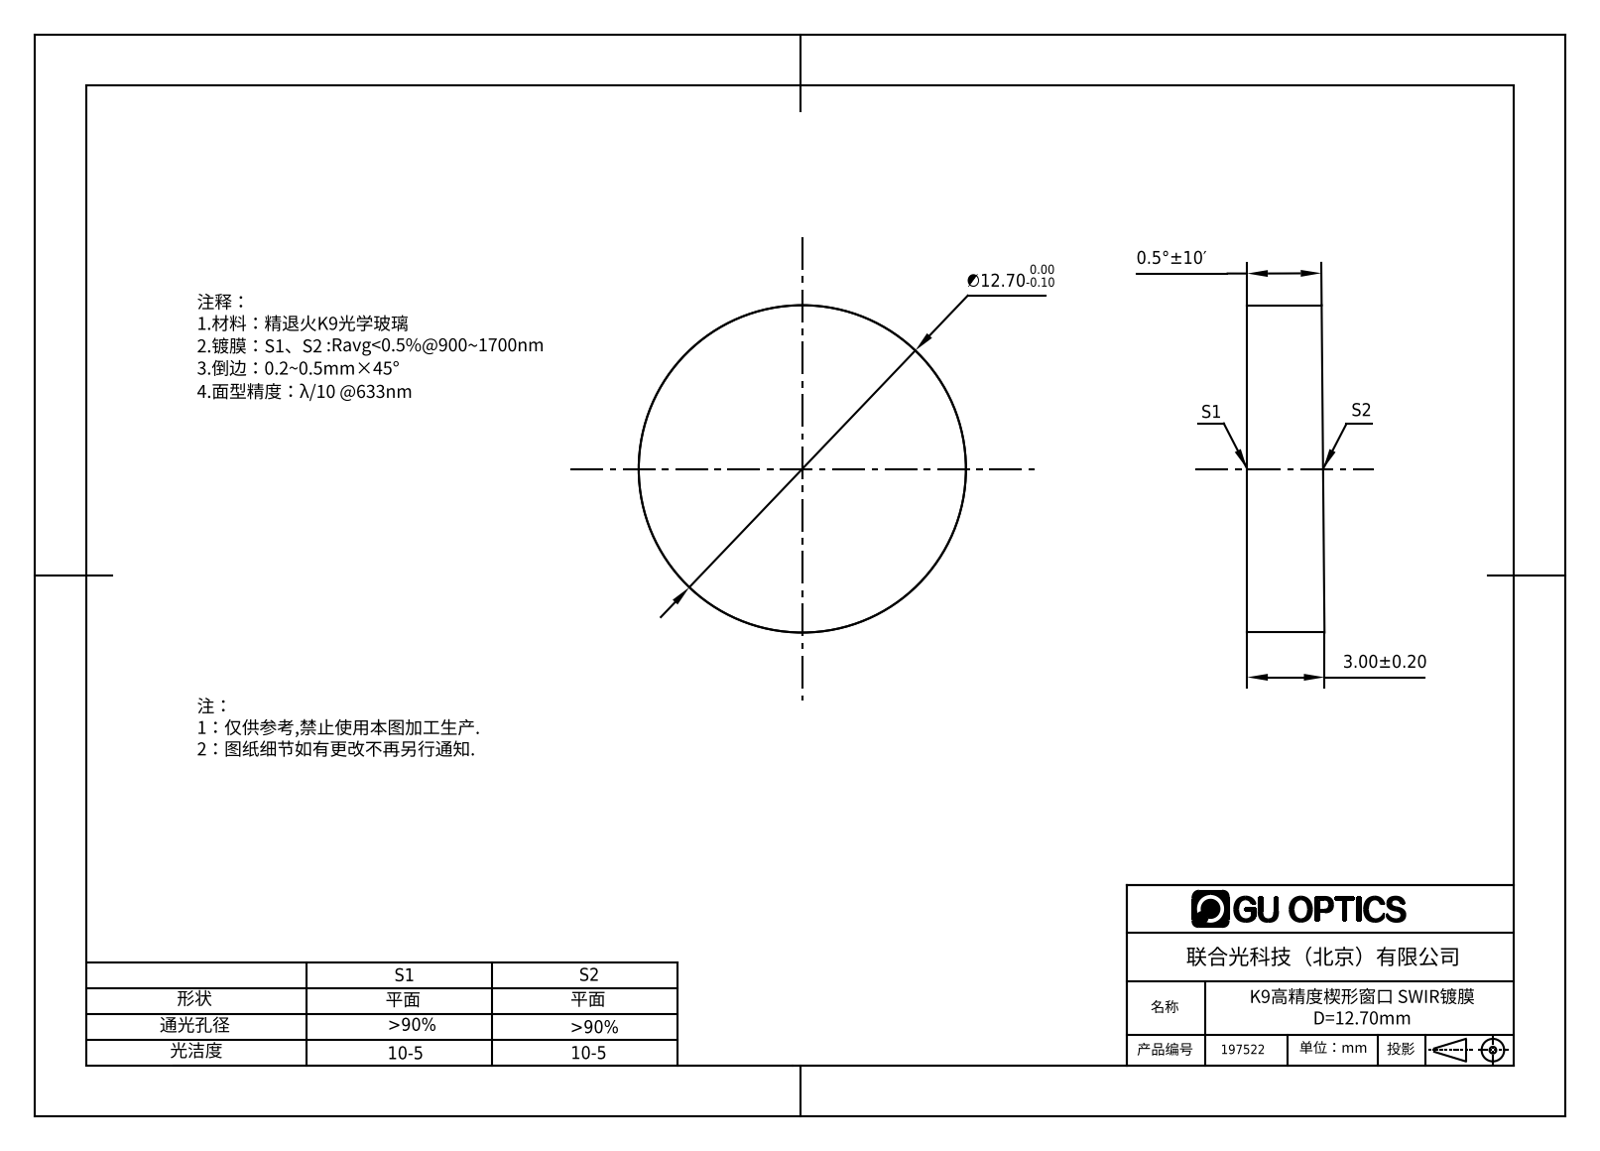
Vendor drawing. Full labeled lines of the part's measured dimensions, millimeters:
Part name (STEP PRODUCT): 197501
STEP written by: SolidWorks 2016 (AUTOMOTIVE_DESIGN)
Units: millimetres
Bodies: 1 solid, 4 faces (2 planar, 2 cylindrical, 0 other)
Overall size (bounding box): 12.7 × 12.7 × 3
Volume: 373 mm³ · Surface area: 371 mm²
Round bosses / shafts (diameter × count): ⌀12.7 ×1
